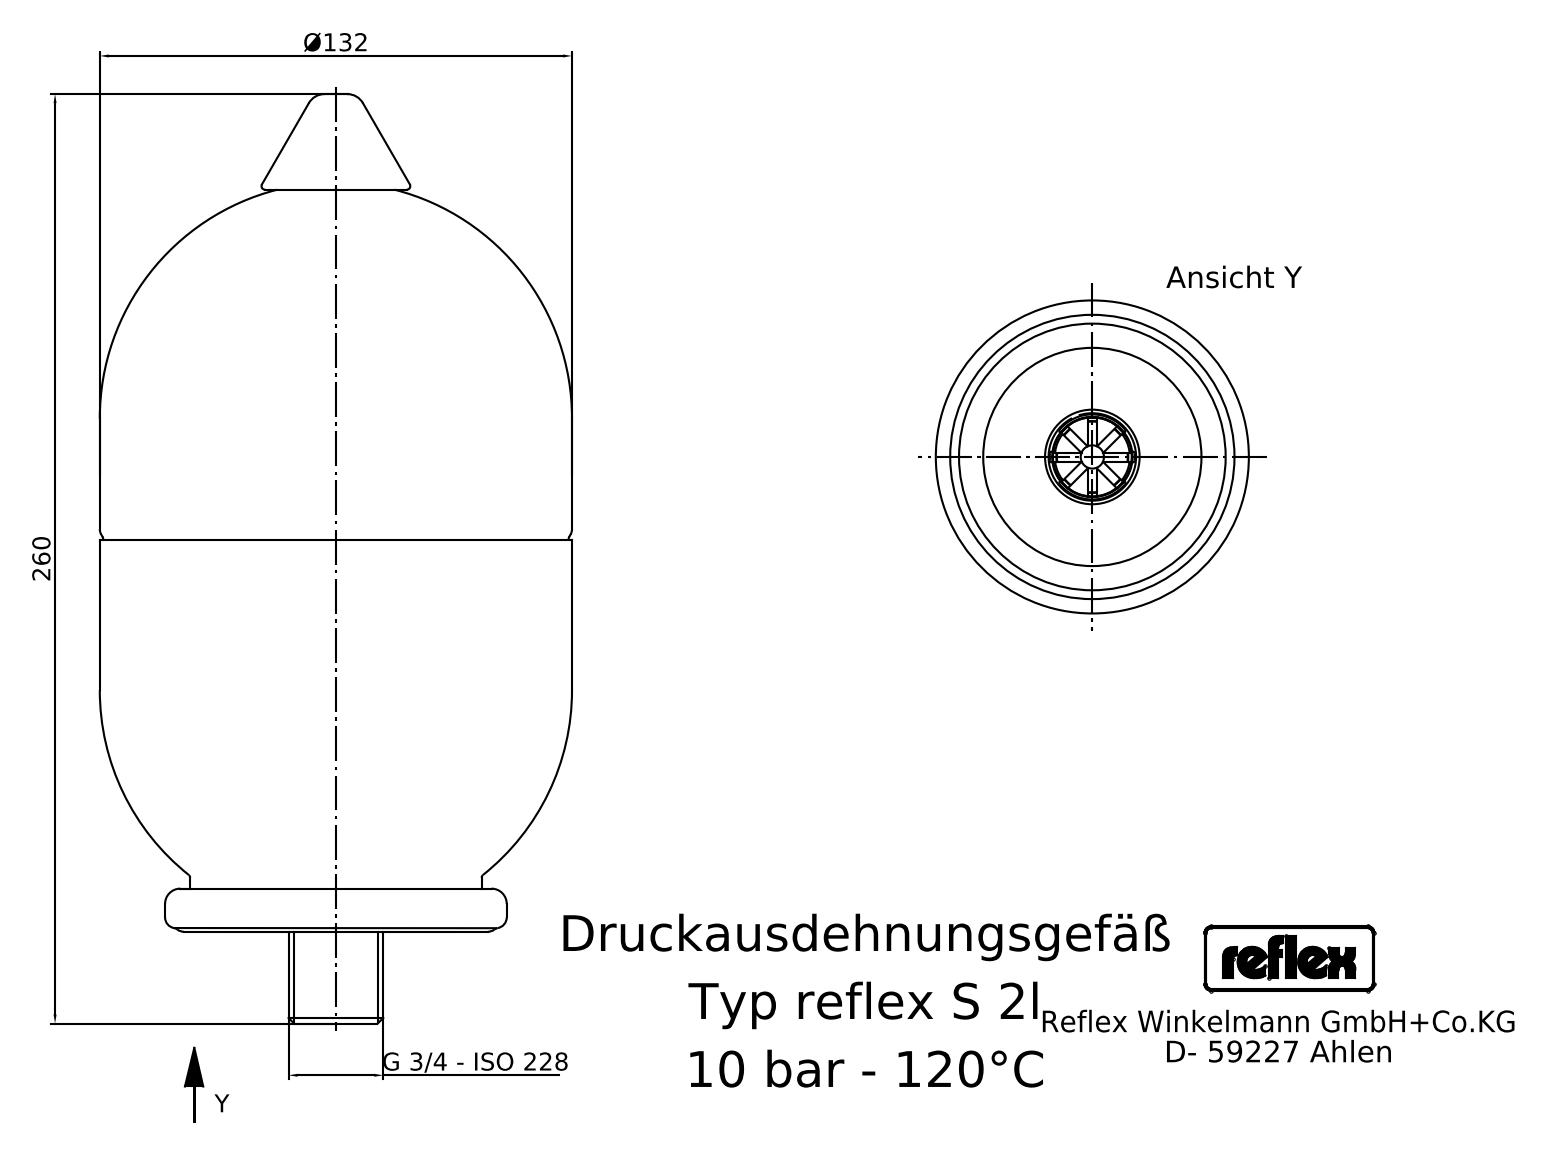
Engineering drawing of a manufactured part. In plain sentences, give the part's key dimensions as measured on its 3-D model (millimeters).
Its 3-D file was written by "Mechanical Desktop 2008 (CONFIG_CONTROL_DESIGN)". It is 13 solids with 150 faces: 72 planar, 44 cylindrical and 34 other. Overall it measures 260 by 132.32 by 132 millimeters. Its volume is 2 480 000 cubic millimeters and its surface area 179 097 square millimeters. Round holes: 1 of diameter 14.1, 1 of diameter 18.9. Round bosses or shafts: 1 of diameter 132, 1 of diameter 96, 1 of diameter 82, 1 of diameter 26.9, 1 of diameter 17.1, 1 of diameter 9, 1 of diameter 6. Partial cylindrical surfaces (rounded edges, fillets, slot ends): 4 of radius 1.12, 3 of radius 0.45, 2 of radius 0.77, 2 of radius 1.35, 2 of radius 1.85, 2 of radius 1.88, 2 of radius 2.54, 1 of radius 0.56. The main face-to-face distances are 0.5, 87, 86.5, 87.5, 36.5, 37, 123.5, 124, 18, 54.5.
